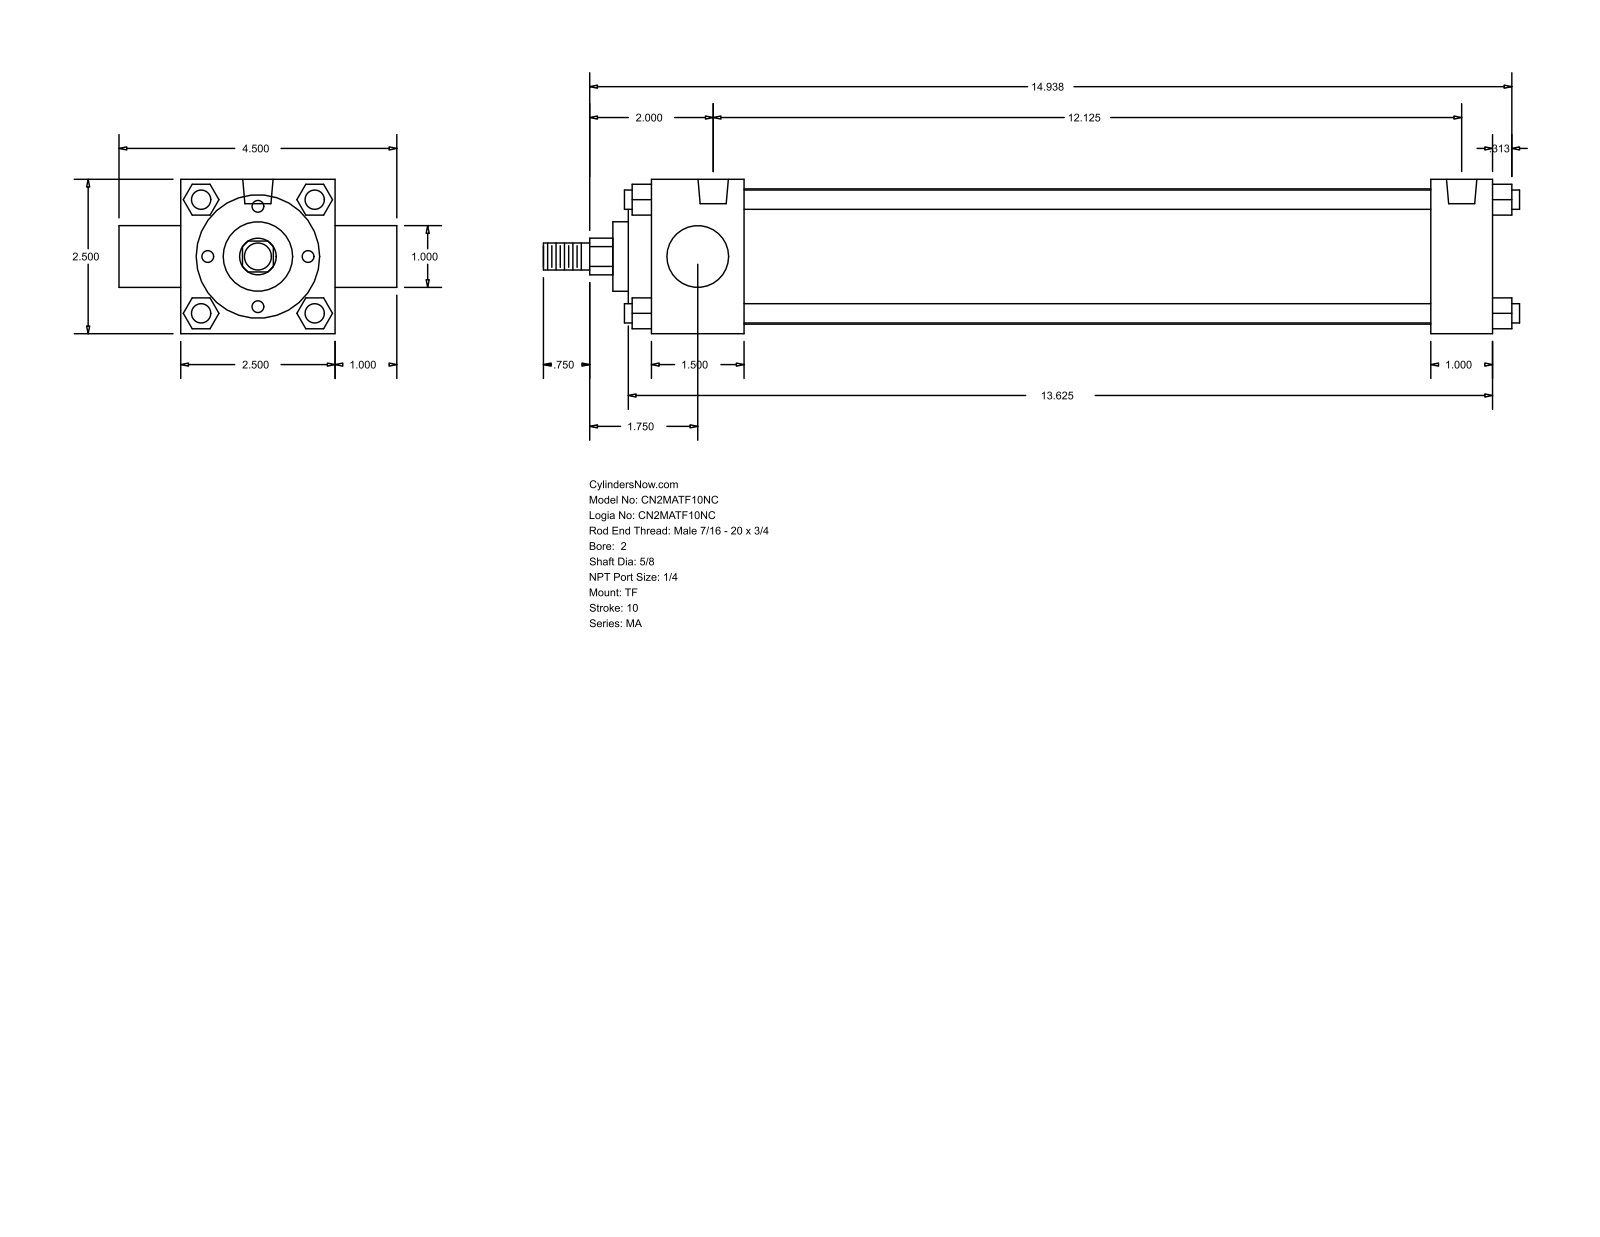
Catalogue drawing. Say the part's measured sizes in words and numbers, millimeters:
The part is named "MA_TF__0200_0.625". Its 3-D file was written by "GSSL Pune (CONFIG_CONTROL_DESIGN)". It is 0 solids with 122 faces: 93 planar, 29 cylindrical and 0 other. Overall it measures 401.64 by 114.3 by 63.5 millimeters. Round holes: 3 of diameter 7.94, 2 of diameter 12.49. Round bosses or shafts: 4 of diameter 7.94, 1 of diameter 55.63, 1 of diameter 50.8, 1 of diameter 28.57, 1 of diameter 25.4, 1 of diameter 15.88, 1 of diameter 11.11. Partial cylindrical surfaces (rounded edges, fillets, slot ends): 1 of radius 7.54. The main face-to-face distances are 63.5, 38.1, 12.7, 346.08, 320.67, 282.57, 307.98, 25.41, 9.52, 47.62. The hole center spacings are 307.97.
